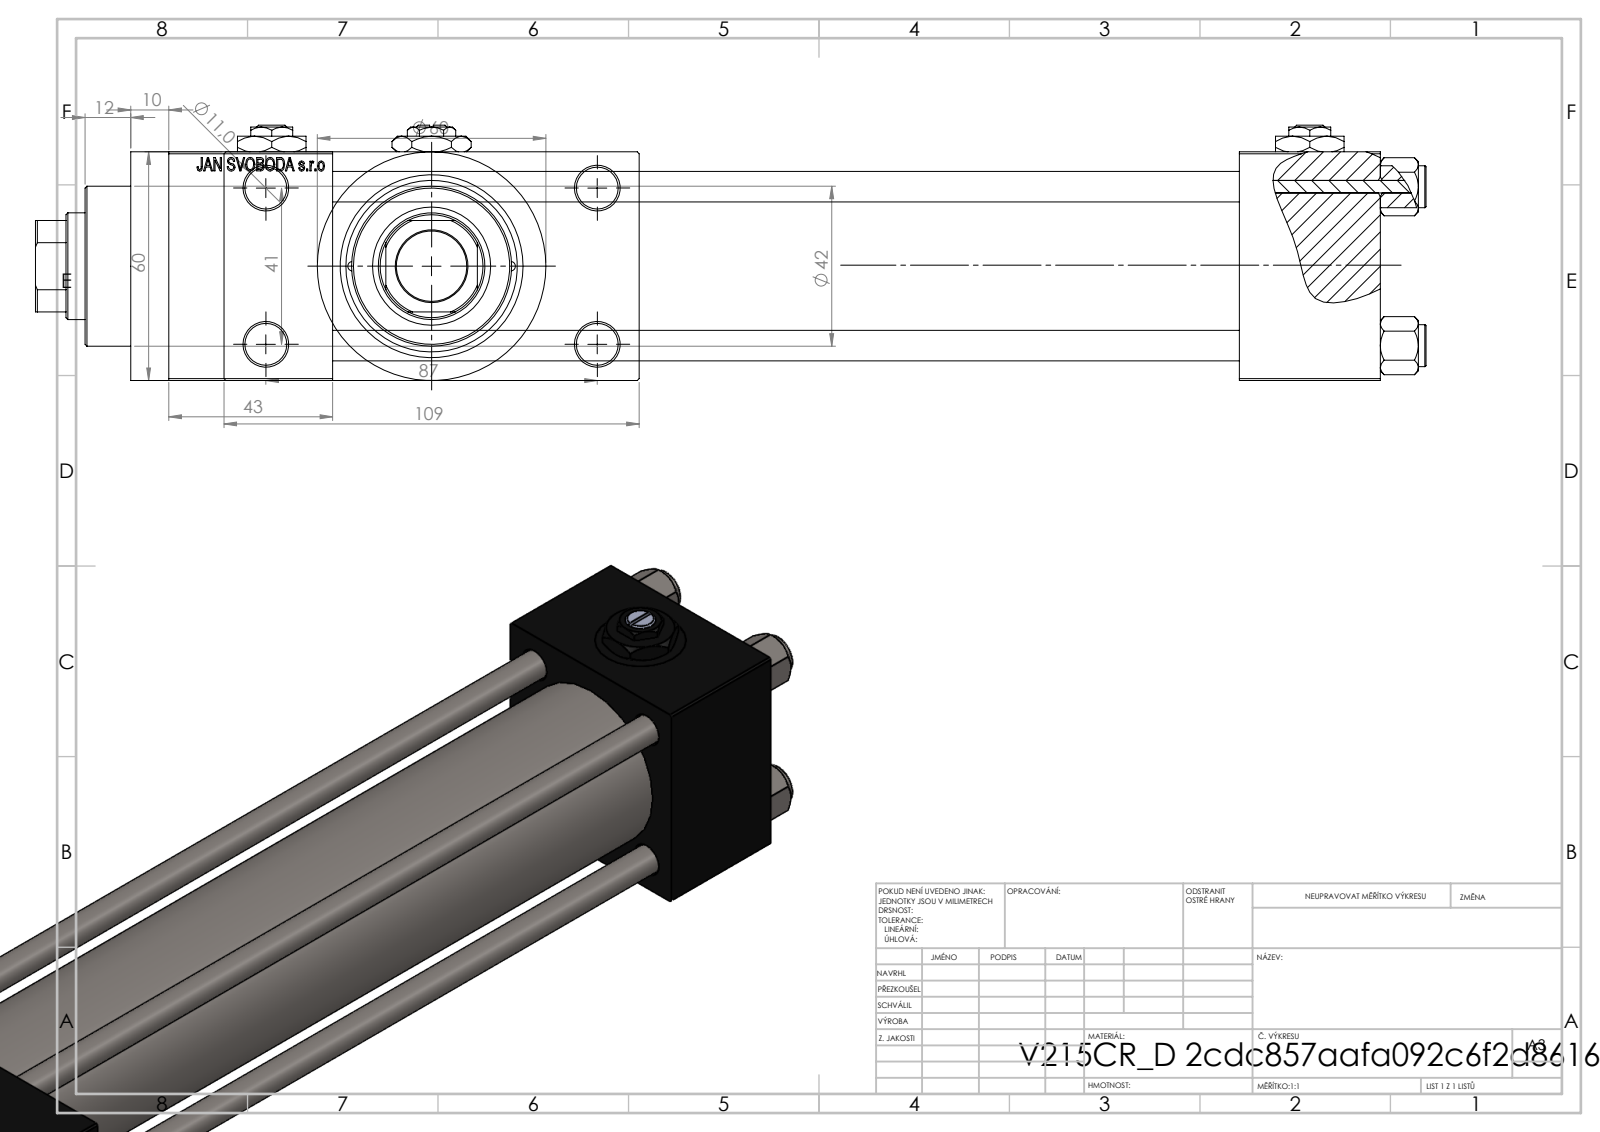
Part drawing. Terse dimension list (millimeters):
name: NUT_M5_D; Zatka_pro_OIL_PORT; V215_VC_A; V215CR_D_TYCINKA (+2 more)
written by: SolidWorks 2019 (CONFIG_CONTROL_DESIGN)
unit: mm
bodies: 13 solids, 1215 faces (550 planar, 103 cylindrical, 562 other)
size: 365 × 109 × 67
volume: 746 454 mm³; area: 214 282 mm²
holes: 4× ⌀8, 4× ⌀11, 4× ⌀16.66, 4× ⌀24, 3× ⌀7, 2× ⌀2.5, 1× ⌀18.5, 1× ⌀28, 1× ⌀31, 1× ⌀40, 1× ⌀45
bosses: 4× ⌀11, 1× ⌀60, 1× ⌀46, 1× ⌀42
rounds: 1× R13.5
face distances: 60, 24.5, 238, 84.5, 37, 275, 318, 281, 43, 109
hole spacings: 20.85, 22.65, 29.49, 30.62, 41.7, 46.53, 47.15, 48.09
